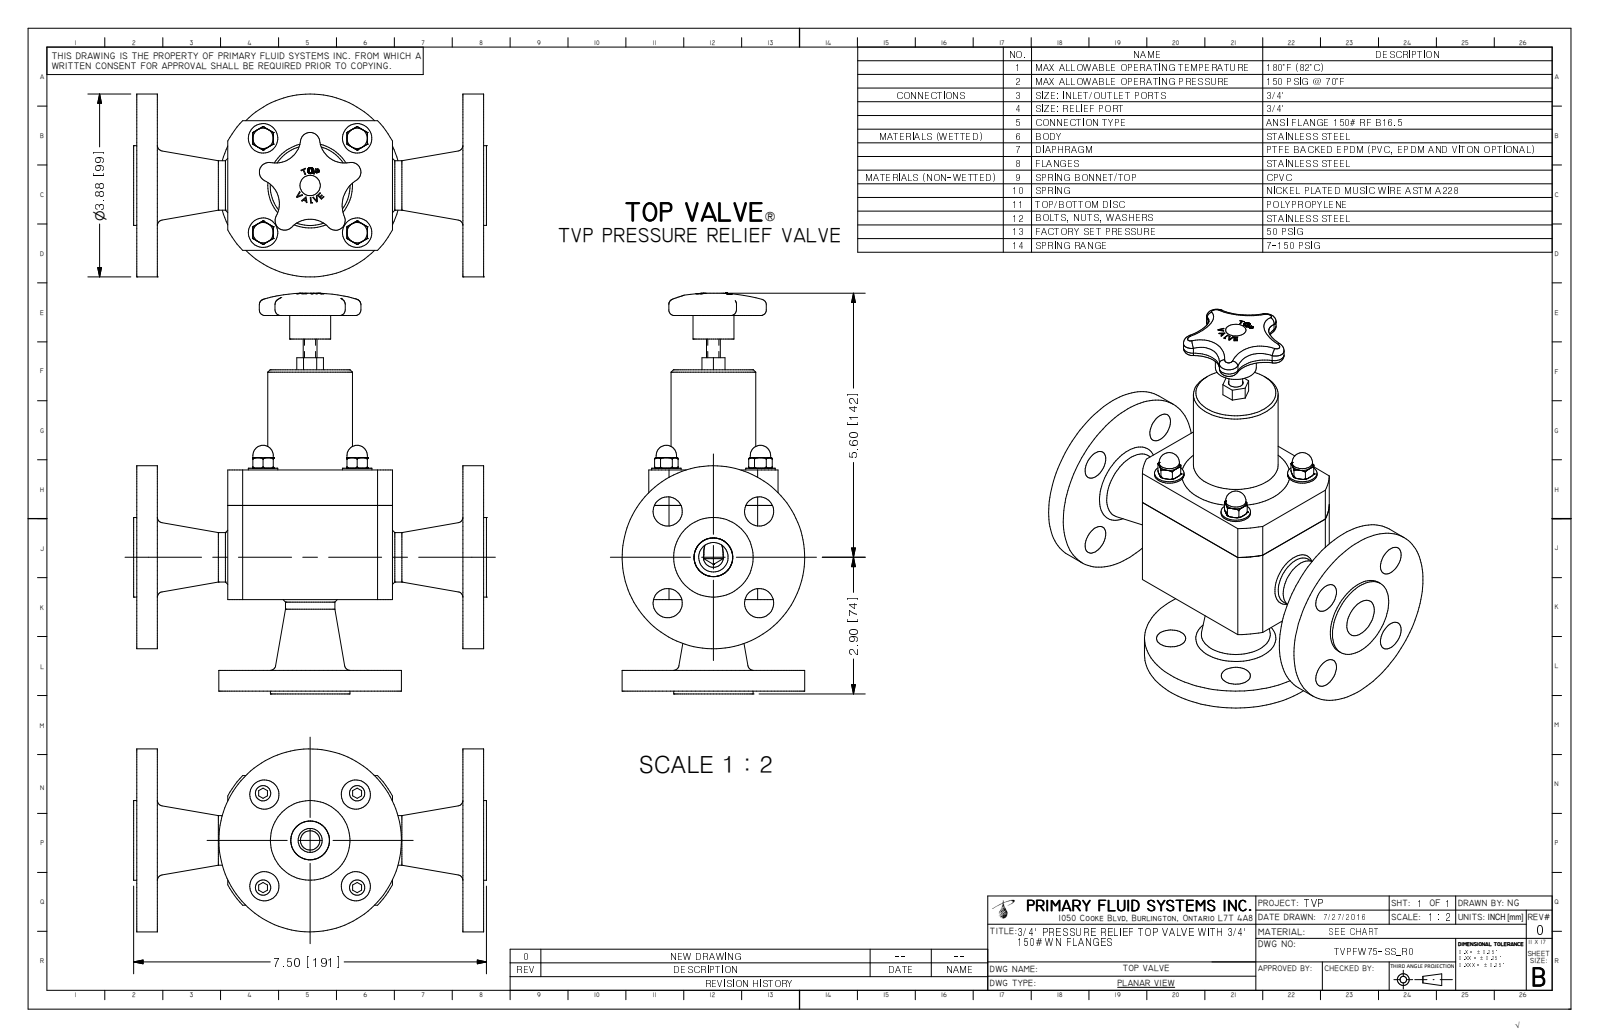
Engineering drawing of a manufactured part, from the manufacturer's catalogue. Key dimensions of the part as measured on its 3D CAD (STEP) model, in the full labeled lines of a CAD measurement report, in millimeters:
Part name (STEP PRODUCT): TVPFW75-SS_R0
STEP written by: Autodesk Inventor 2009 (AUTOMOTIVE_DESIGN)
Units: millimetres
Bodies: 1 solid, 352 faces (132 planar, 65 cylindrical, 155 other)
Overall size (bounding box): 215.9 × 190.5 × 98.6
Volume: 812 500 mm³ · Surface area: 124 600 mm²
Round holes (diameter × count): ⌀15.7 ×8, ⌀4.4 ×4, ⌀20.9 ×2, ⌀61 ×1
Round bosses / shafts (diameter × count): ⌀15.9 ×4, ⌀11 ×4, ⌀98.6 ×2, ⌀42.9 ×2, ⌀26.7 ×2, ⌀60.3 ×1, ⌀45.7 ×1, ⌀22.1 ×1
Partial cylindrical surfaces — rounded edges, fillets, slot ends (radius × count): R2.2 ×5, R5.2 ×5, R13.6 ×4, R16.7 ×4, R15.9 ×1, R18.9 ×1, R50.5 ×1
Main face-to-face distances: 11.2, 176.1, 49.2, 138.1, 38, 126.9, 49.2, 187.3, 11.2, 38
Hole centre spacings: 34.9, 49.4, 50.1, 1, 35.9, 50.8, 69.9, 70.8
